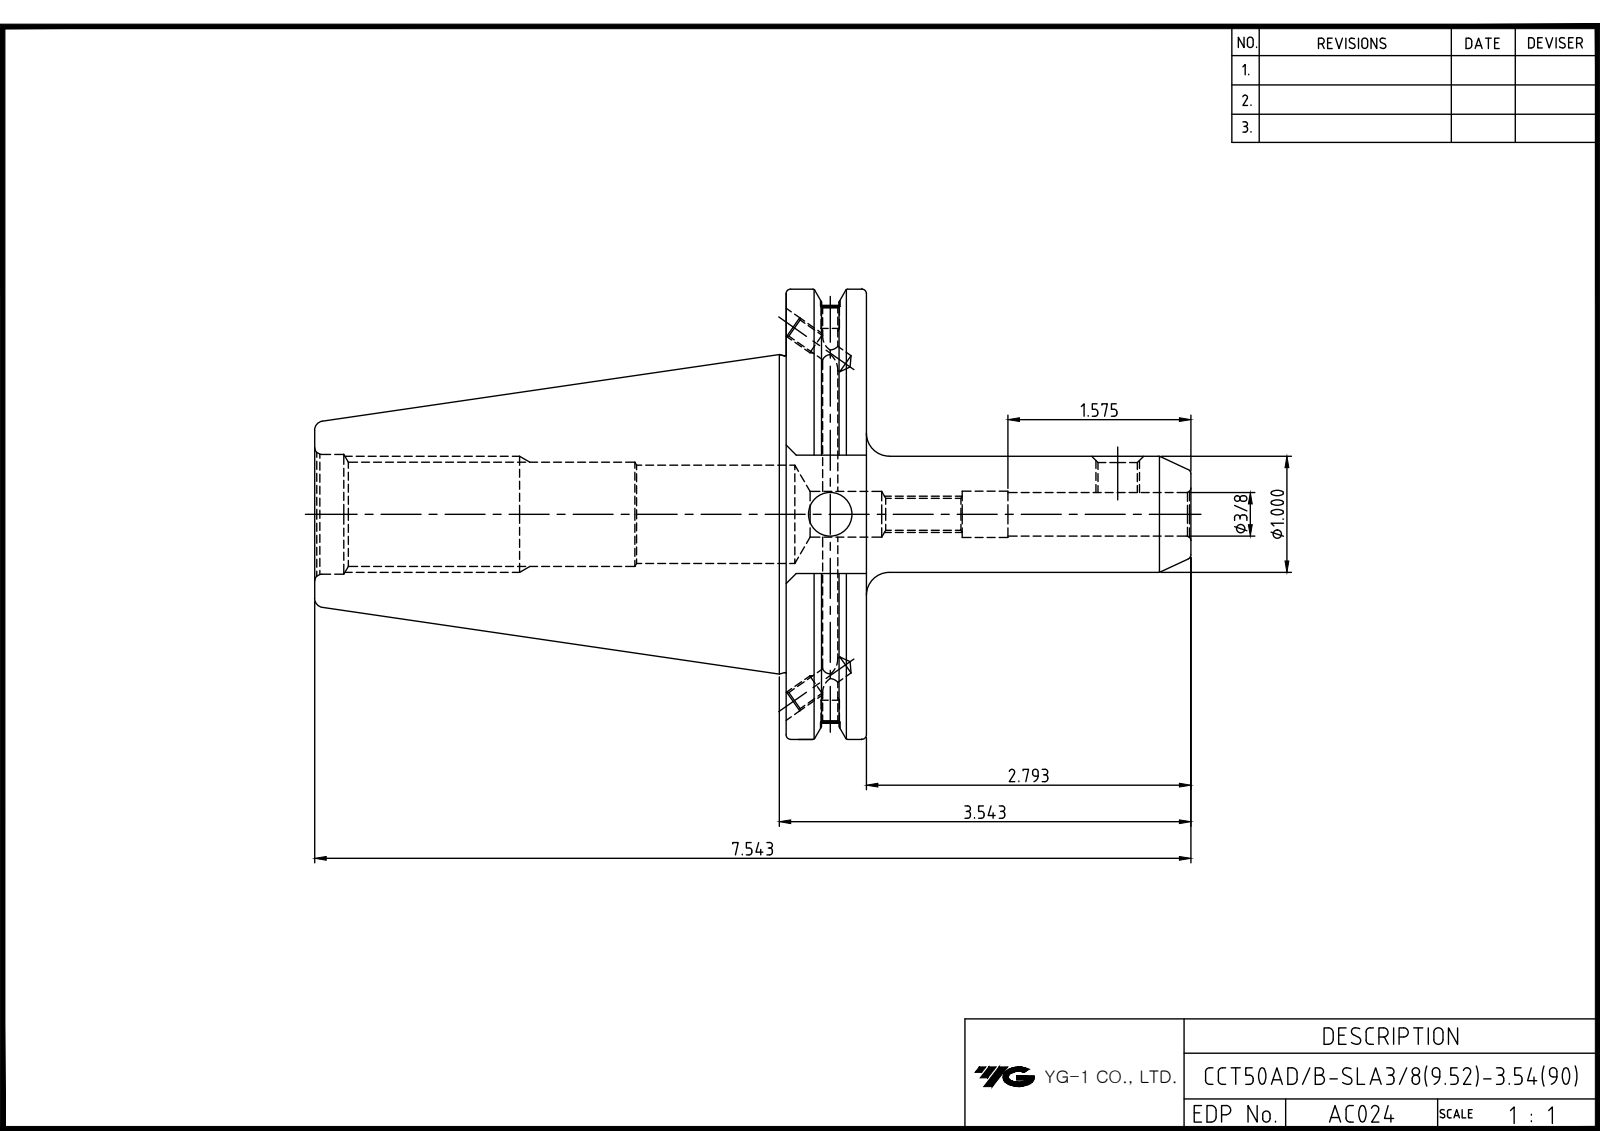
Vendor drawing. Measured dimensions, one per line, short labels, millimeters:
name: LO-CCT50ADB-SLA9.525-90
written by: Autodesk Inventor 2025 (AUTOMOTIVE_DESIGN)
unit: mm
bodies: 1 solid, 92 faces (39 planar, 28 cylindrical, 25 other)
size: 191.6 × 98.42 × 94.69
volume: 357 643 mm³; area: 52 530 mm²
holes: 2× ⌀3.24, 2× ⌀4.13, 2× ⌀4.2, 2× ⌀5, 2× ⌀9.53, 1× ⌀6.78, 1× ⌀8.38, 1× ⌀10, 1× ⌀10.72, 1× ⌀21.97, 1× ⌀26.2
bosses: 1× ⌀98.42, 1× ⌀91.29, 1× ⌀69.25, 1× ⌀25.4
face distances: 17.55, 103.1, 120.65, 73.03, 25.9, 103.5, 0.4, 17.15, 114.64, 11.54
